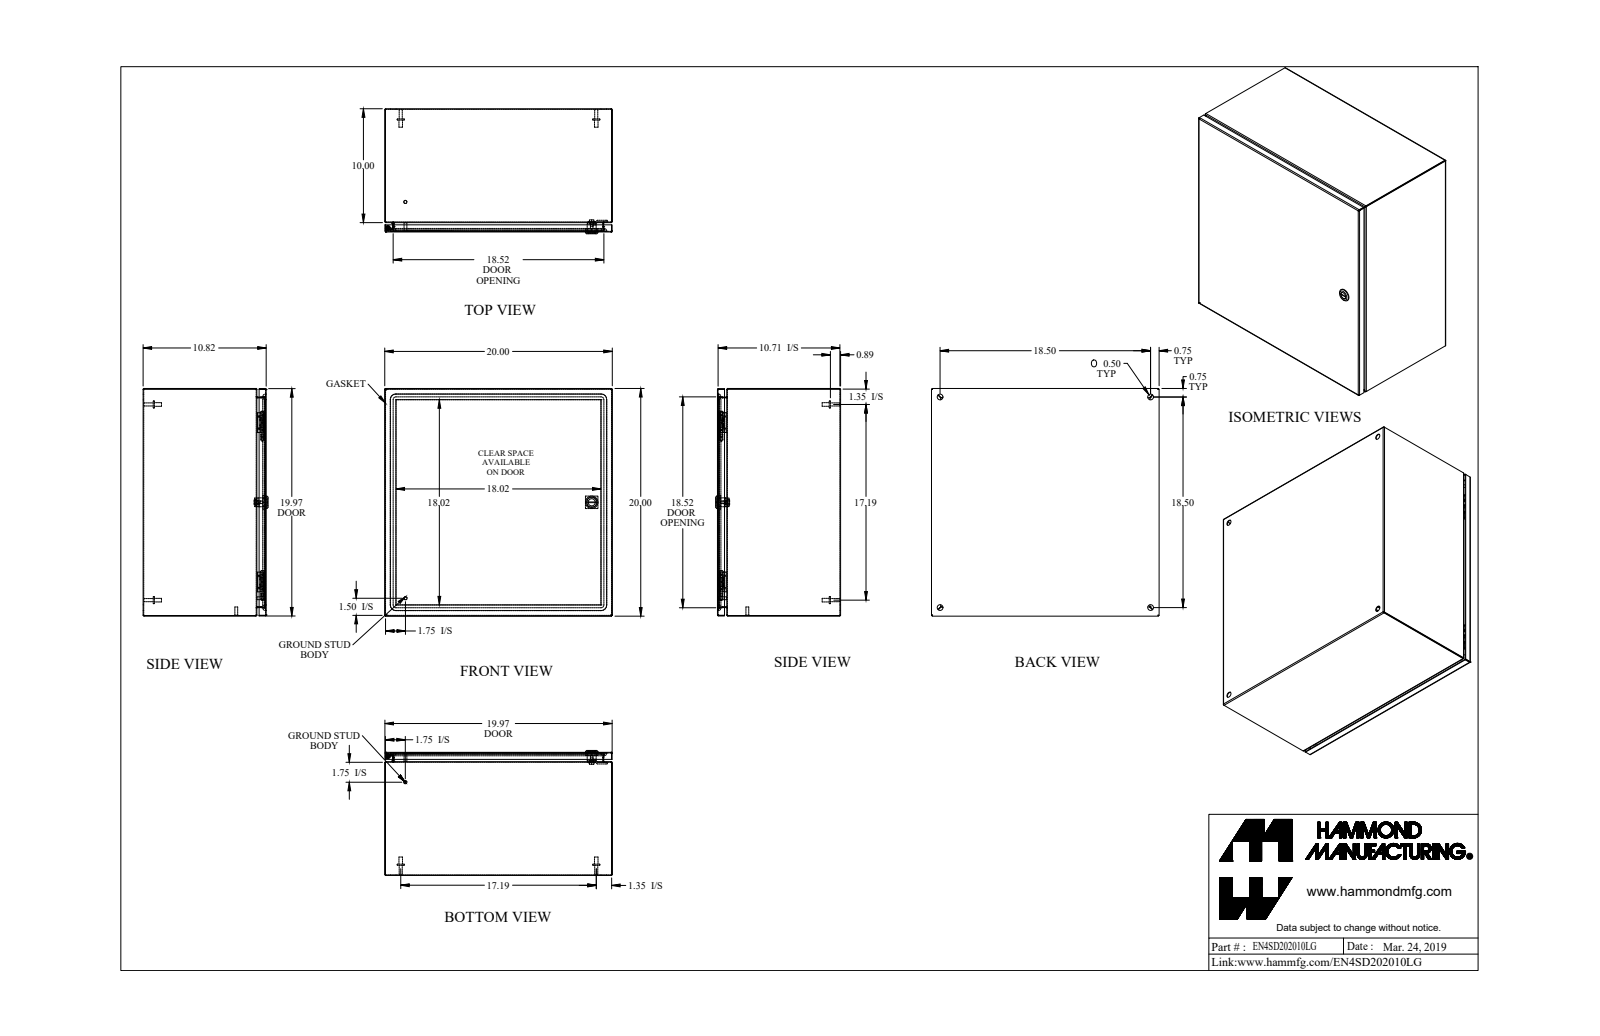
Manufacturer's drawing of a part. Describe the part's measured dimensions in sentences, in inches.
The part is named "EN4SD202010LG_Default". Its 3-D file was written by "SolidWorks 2019 (CONFIG_CONTROL_DESIGN)". It is 21 solids with 634 faces: 285 planar, 213 cylindrical and 136 other. Overall it measures 20 by 20 by 10.982 inches. Its volume is 107.9 cubic inches and its surface area 3 687 square inches. Round holes: 4 of diameter 0.5, 1 of diameter 0.172, 1 of diameter 0.232, 1 of diameter 0.24, 1 of diameter 0.242, 1 of diameter 0.625, 1 of diameter 0.785. Round bosses or shafts: 4 of diameter 0.625, 4 of diameter 0.313, 4 of diameter 0.27, 2 of diameter 0.281, 2 of diameter 0.25, 1 of diameter 1.1, 1 of diameter 0.525, 1 of diameter 0.455. Partial cylindrical surfaces (rounded edges, fillets, slot ends): 21 of radius 0.029, 21 of radius 0.086, 16 of radius 0.25, 8 of radius 19, 4 of radius 0.006, 4 of radius 0.062, 4 of radius 0.499, 2 of radius 0.125. The main face-to-face distances are 0.057, 10.765, 19.943, 19.886, 10.708, 10.822, 20, 0.822, 9.943, 0.749. The hole center spacings are 18.5, 26.163, 9.31, 9.311, 19.742, 19.742.
